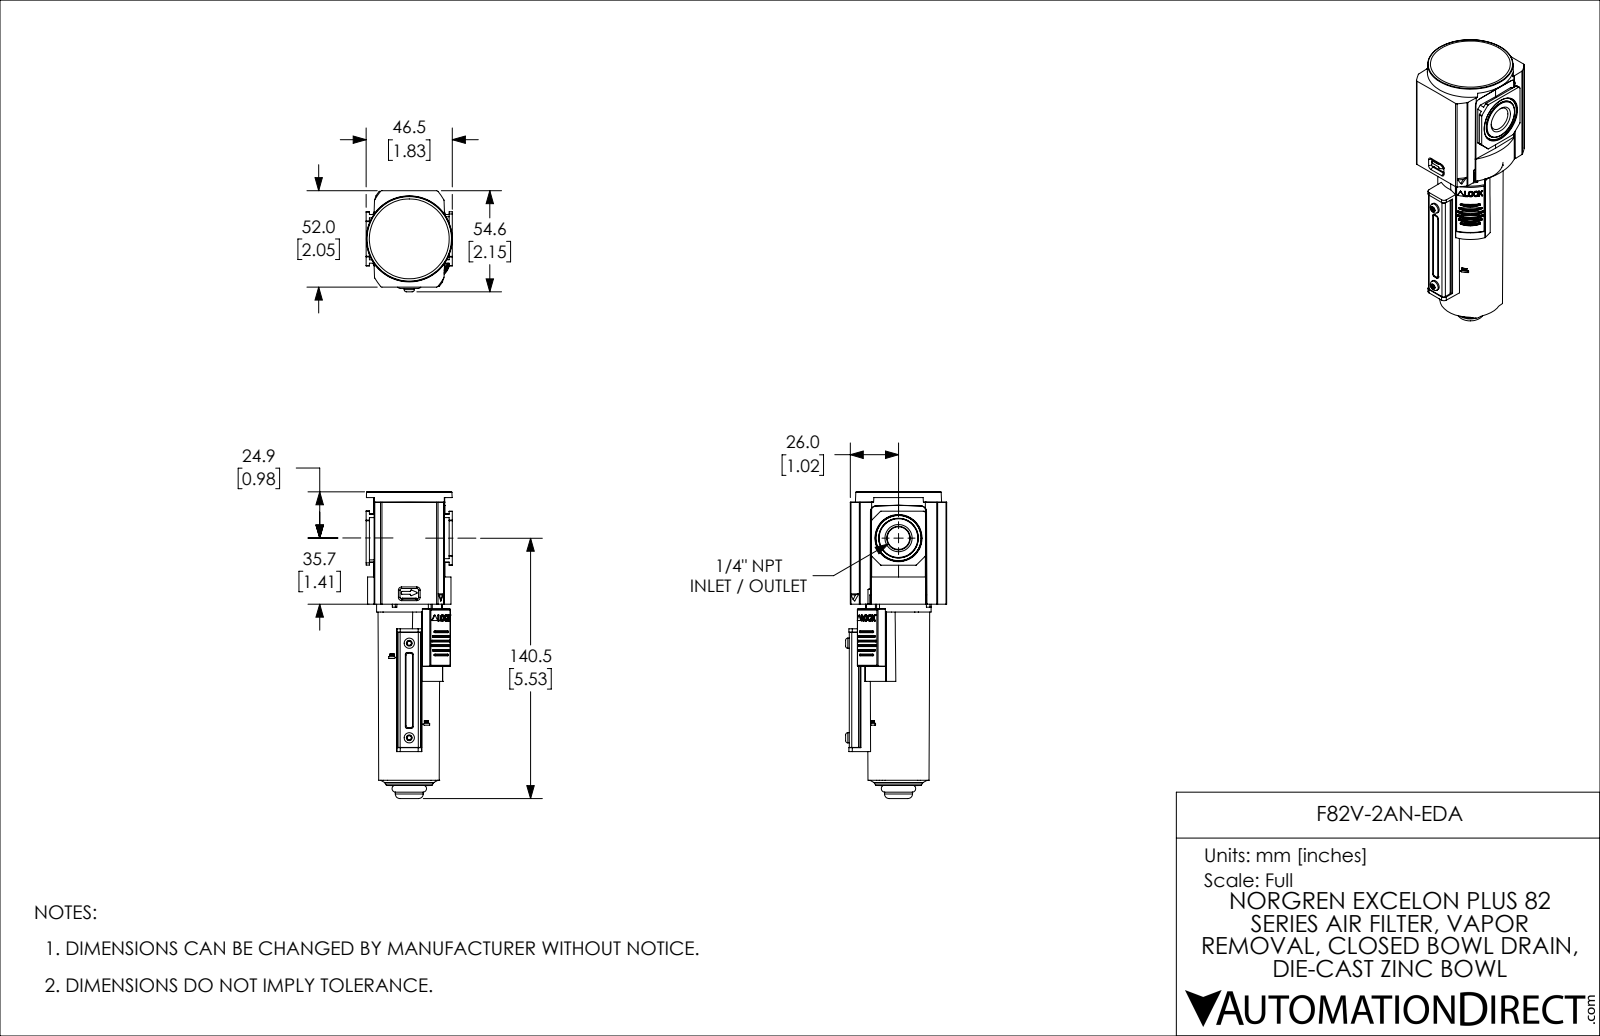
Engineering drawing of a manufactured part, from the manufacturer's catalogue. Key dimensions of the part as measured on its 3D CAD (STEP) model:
Part name (STEP PRODUCT): F82V-2AN-EDA
STEP written by: SolidWorks 2021 (CONFIG_CONTROL_DESIGN)
Units: inches
Bodies: 5 solids, 1012 faces (441 planar, 394 cylindrical, 177 other)
Overall size (bounding box): 6.515 × 2.148 × 1.831
Volume: 12.68 in³ · Surface area: 88.13 in²
Round holes (diameter × count): ⌀0.059 ×2, ⌀0.128 ×2, ⌀0.628 ×1
Round bosses / shafts (diameter × count): ⌀0.217 ×2, ⌀1.388 ×1, ⌀1.356 ×1, ⌀1.291 ×1, ⌀1.257 ×1, ⌀0.906 ×1, ⌀0.626 ×1, ⌀0.594 ×1
Partial cylindrical surfaces — rounded edges, fillets, slot ends (radius × count): R0.02 ×53, R0.039 ×38, R0.011 ×12, R0.019 ×12, R0.01 ×10, R0.031 ×8, R0.036 ×8, R0.048 ×8
Main face-to-face distances: 0.059, 1.988, 2.047, 1.929, 0.058, 2.093, 2.151, 0.182, 0.236, 1.352
Hole centre spacings: 0.797, 0.531, 0.594, 1.063, 1.189
